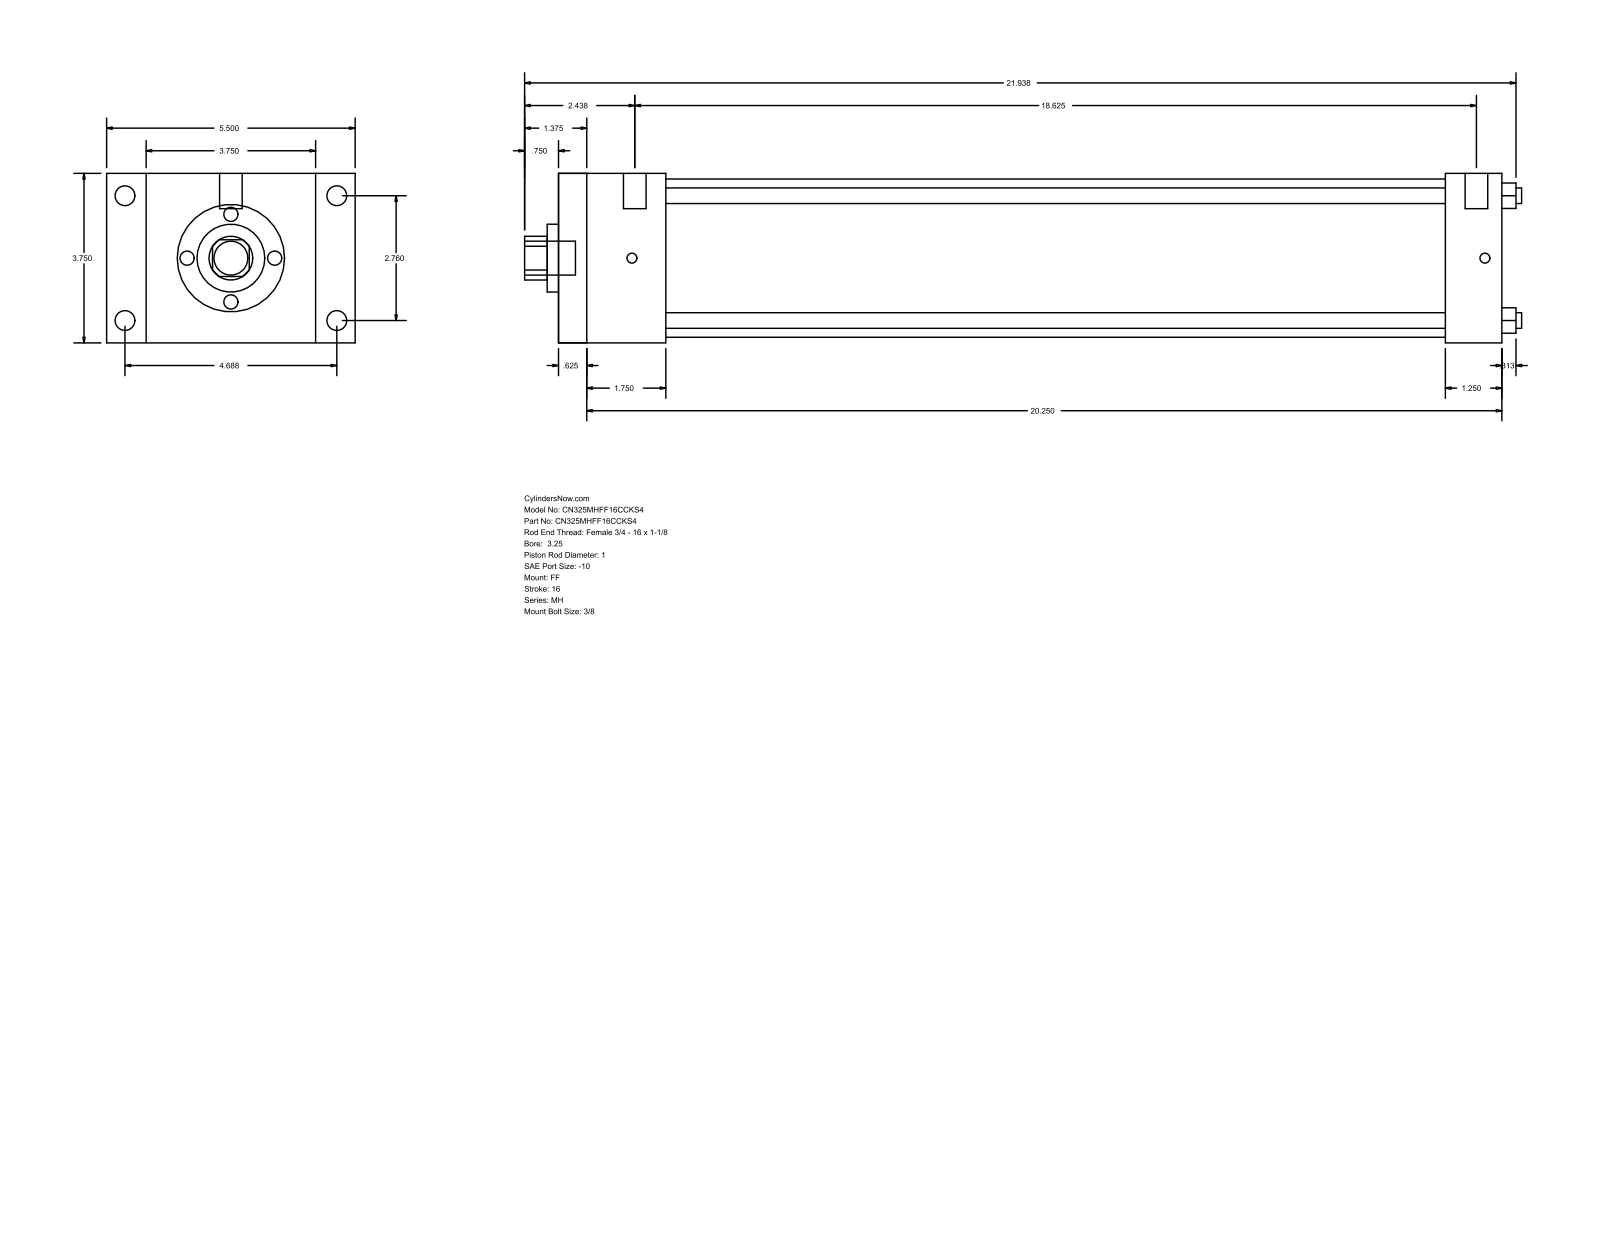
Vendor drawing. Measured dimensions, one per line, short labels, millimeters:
name: MH_FF__0325_1
written by: GSSL Pune (CONFIG_CONTROL_DESIGN)
unit: mm
bodies: 0 solids, 92 faces (64 planar, 28 cylindrical, 0 other)
size: 560.39 × 139.7 × 95.25
holes: 4× ⌀8.76, 1× ⌀25.4, 1× ⌀38.1, 1× ⌀88.9
bosses: 4× ⌀11.13, 4× ⌀5.56, 2× ⌀12.7, 1× ⌀19.05
rounds: 1× R12.29
face distances: 95.24, 530.22, 15.87, 514.35, 22.23, 117.47, 498.47, 482.6, 31.75, 60.33
hole spacings: 49.57, 70.1, 99.14
